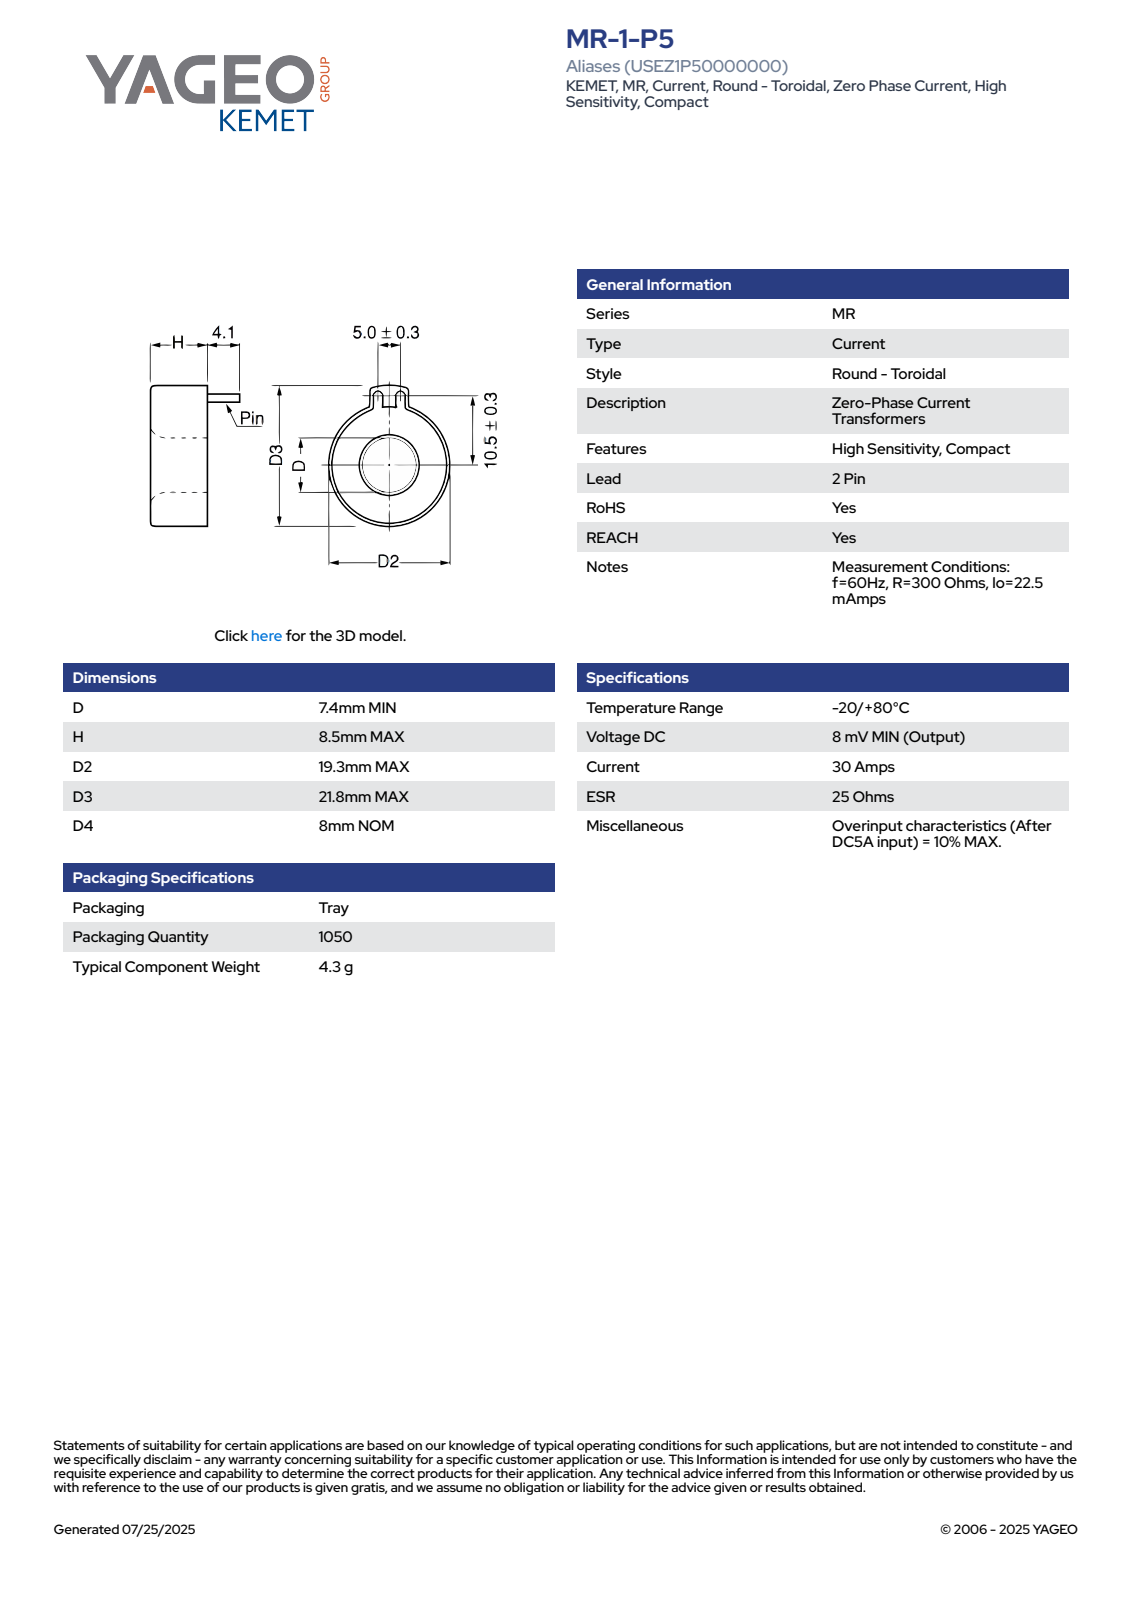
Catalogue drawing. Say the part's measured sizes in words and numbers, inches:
The part is named "Default". Its 3-D file was written by "SolidWorks 2014 (AUTOMOTIVE_DESIGN)". It is 1 solid with 77 faces: 28 planar, 12 cylindrical and 37 other. Overall it measures 0.858 by 0.76 by 0.496 inches. Its volume is 0.139 cubic inches and its surface area 2.021 square inches. Round holes: 1 of diameter 0.291. Round bosses or shafts: 2 of diameter 0.039, 1 of diameter 0.76. Partial cylindrical surfaces (rounded edges, fillets, slot ends): 2 of radius 0.02, 1 of radius 0.38. The main face-to-face distances are 0.335, 0.292, 0.161, 0.496, 0.359, 0.197, 0.137, 0.279, 0.118, 0.08.
